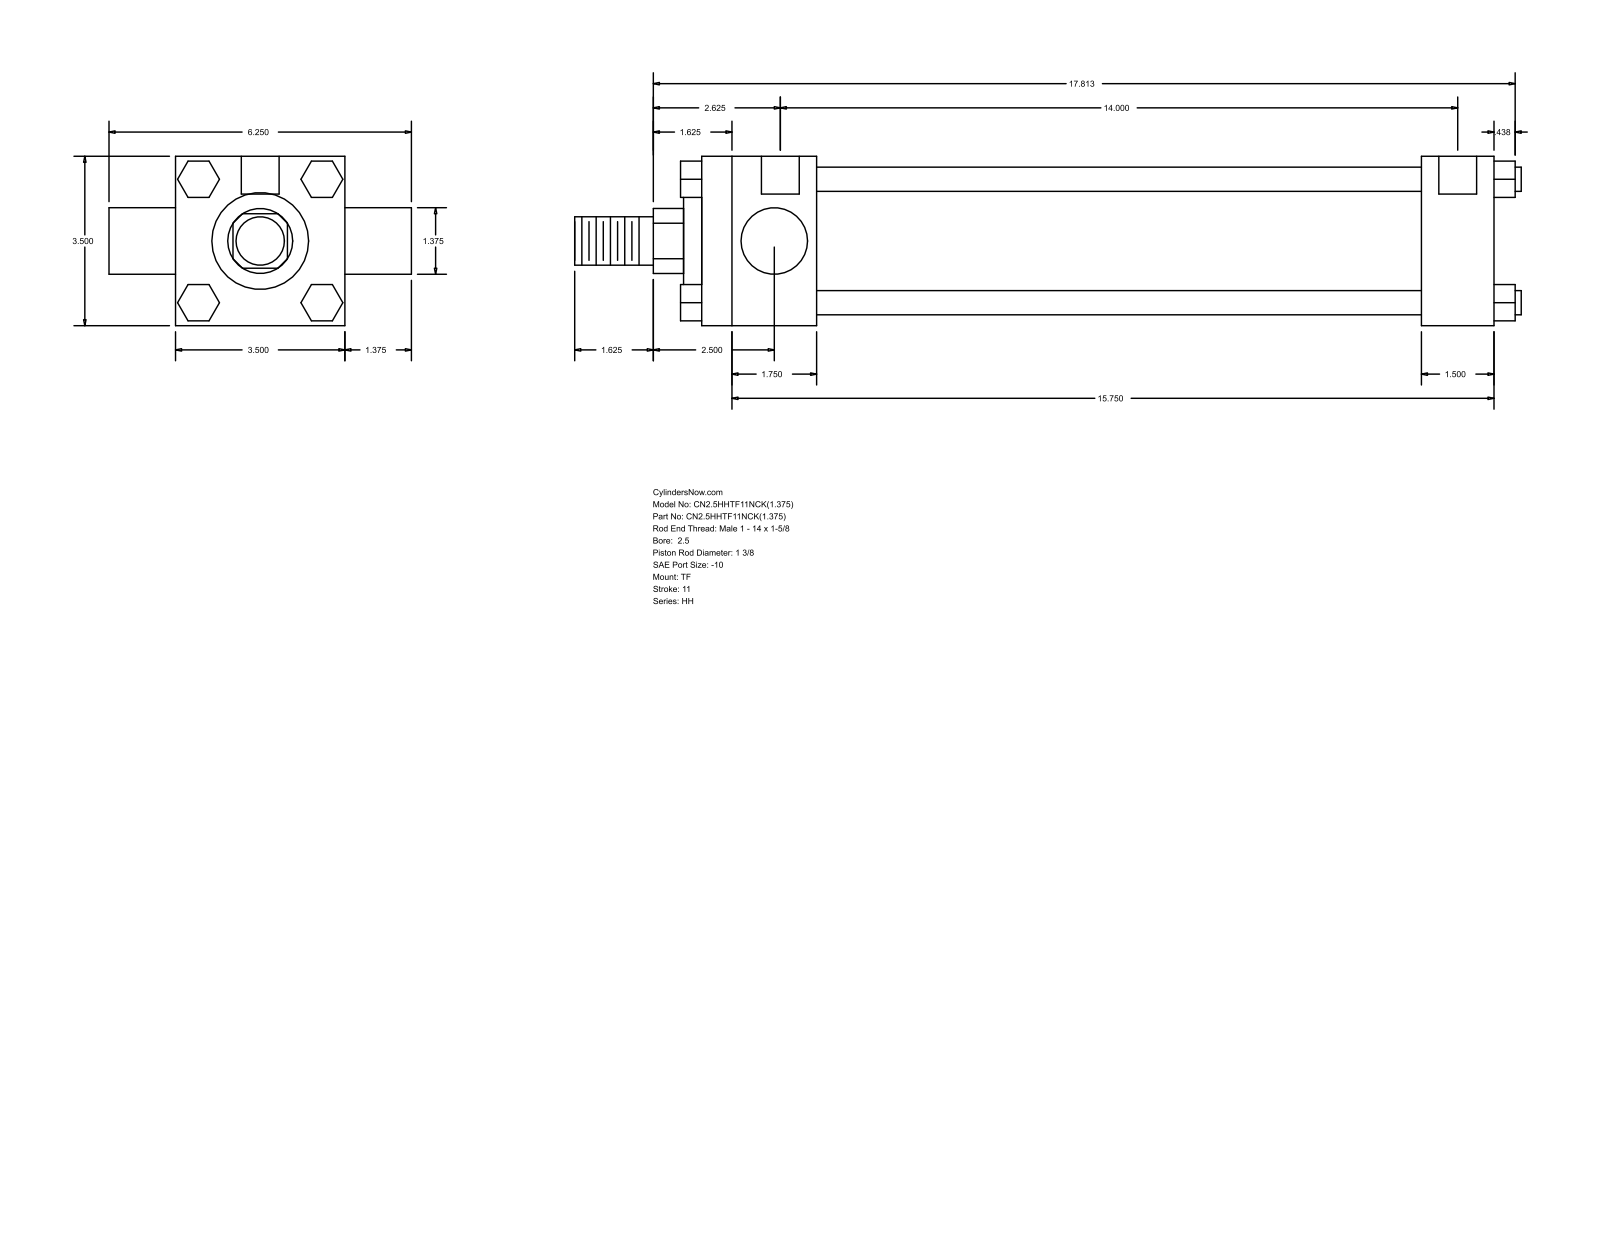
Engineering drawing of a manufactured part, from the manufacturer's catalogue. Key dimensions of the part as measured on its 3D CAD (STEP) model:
Part name (STEP PRODUCT): HH_TF__0250_1.375
STEP written by: GSSL Pune (CONFIG_CONTROL_DESIGN)
Units: millimetres
Bodies: 0 solids, 120 faces (92 planar, 28 cylindrical, 0 other)
Overall size (bounding box): 496.89 × 158.75 × 88.9
Round holes (diameter × count): ⌀5.56 ×3, ⌀19.84 ×2
Round bosses / shafts (diameter × count): ⌀12.7 ×4, ⌀34.92 ×2, ⌀73.03 ×1, ⌀50.8 ×1, ⌀25.4 ×1
Partial cylindrical surfaces — rounded edges, fillets, slot ends (radius × count): R17.06 ×1
Main face-to-face distances: 88.9, 415.92, 60.32, 355.6, 377.83, 317.51, 38.09, 19.05, 32.38, 56.09
Hole centre spacings: 1.58, 1.59, 355.6, 357.18, 357.19, 358.77
